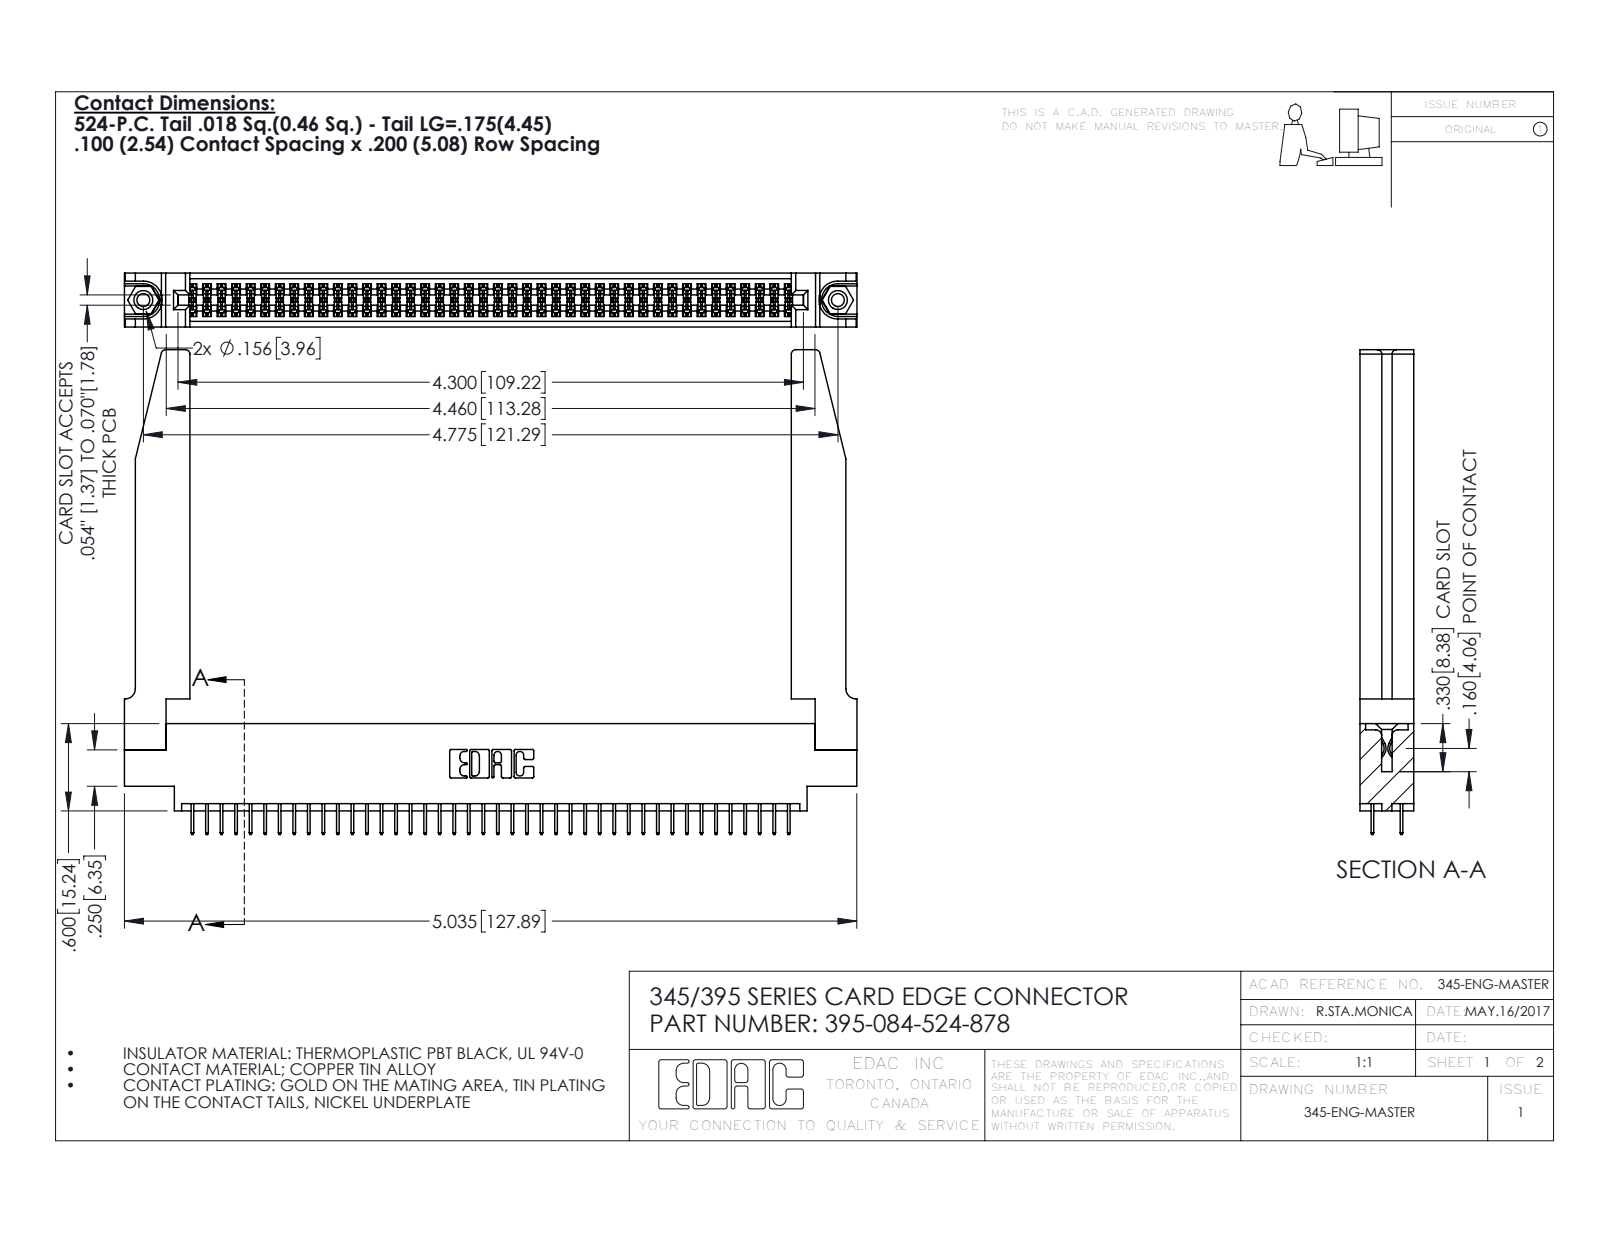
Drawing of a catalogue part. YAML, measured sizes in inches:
part_name: "345-292-001_345-293-124; 345 Part_0.170 Offset - 0.156 Dia-TH; 345-250-001_345-250-001-102; 395-084-524-878 (+1 more)"
step_written_by: "SolidWorks 2016 (CONFIG_CONTROL_DESIGN)"
units: inches
bodies: {solids: 89, faces: 4900, planar: 3502, cylindrical: 1346, other: 52}
overall_size: [5.036, 3.332, 0.37]
volume: 1.218
surface_area: 38.22
round_holes:
  - {diameter: 0.089, count: 2}
  - {diameter: 0.125, count: 2}
  - {diameter: 0.156, count: 2}
  - {diameter: 0.064, count: 1}
round_bosses_or_shafts:
  - {diameter: 0.155, count: 2}
partial_cylinders:
  - {radius: 0.006, count: 126}
  - {radius: 0.01, count: 22}
  - {radius: 0.03, count: 8}
  - {radius: 0.007, count: 6}
  - {radius: 0.031, count: 6}
  - {radius: 0.026, count: 3}
  - {radius: 0.014, count: 2}
  - {radius: 0.019, count: 2}
face_to_face_distances: [0.37, 0.072, 0.298, 0.098, 0.272, 0.025, 0.2, 0.225, 0.175, 0.148]
hole_center_spacings: [0.27, 4.539, 4.775]
